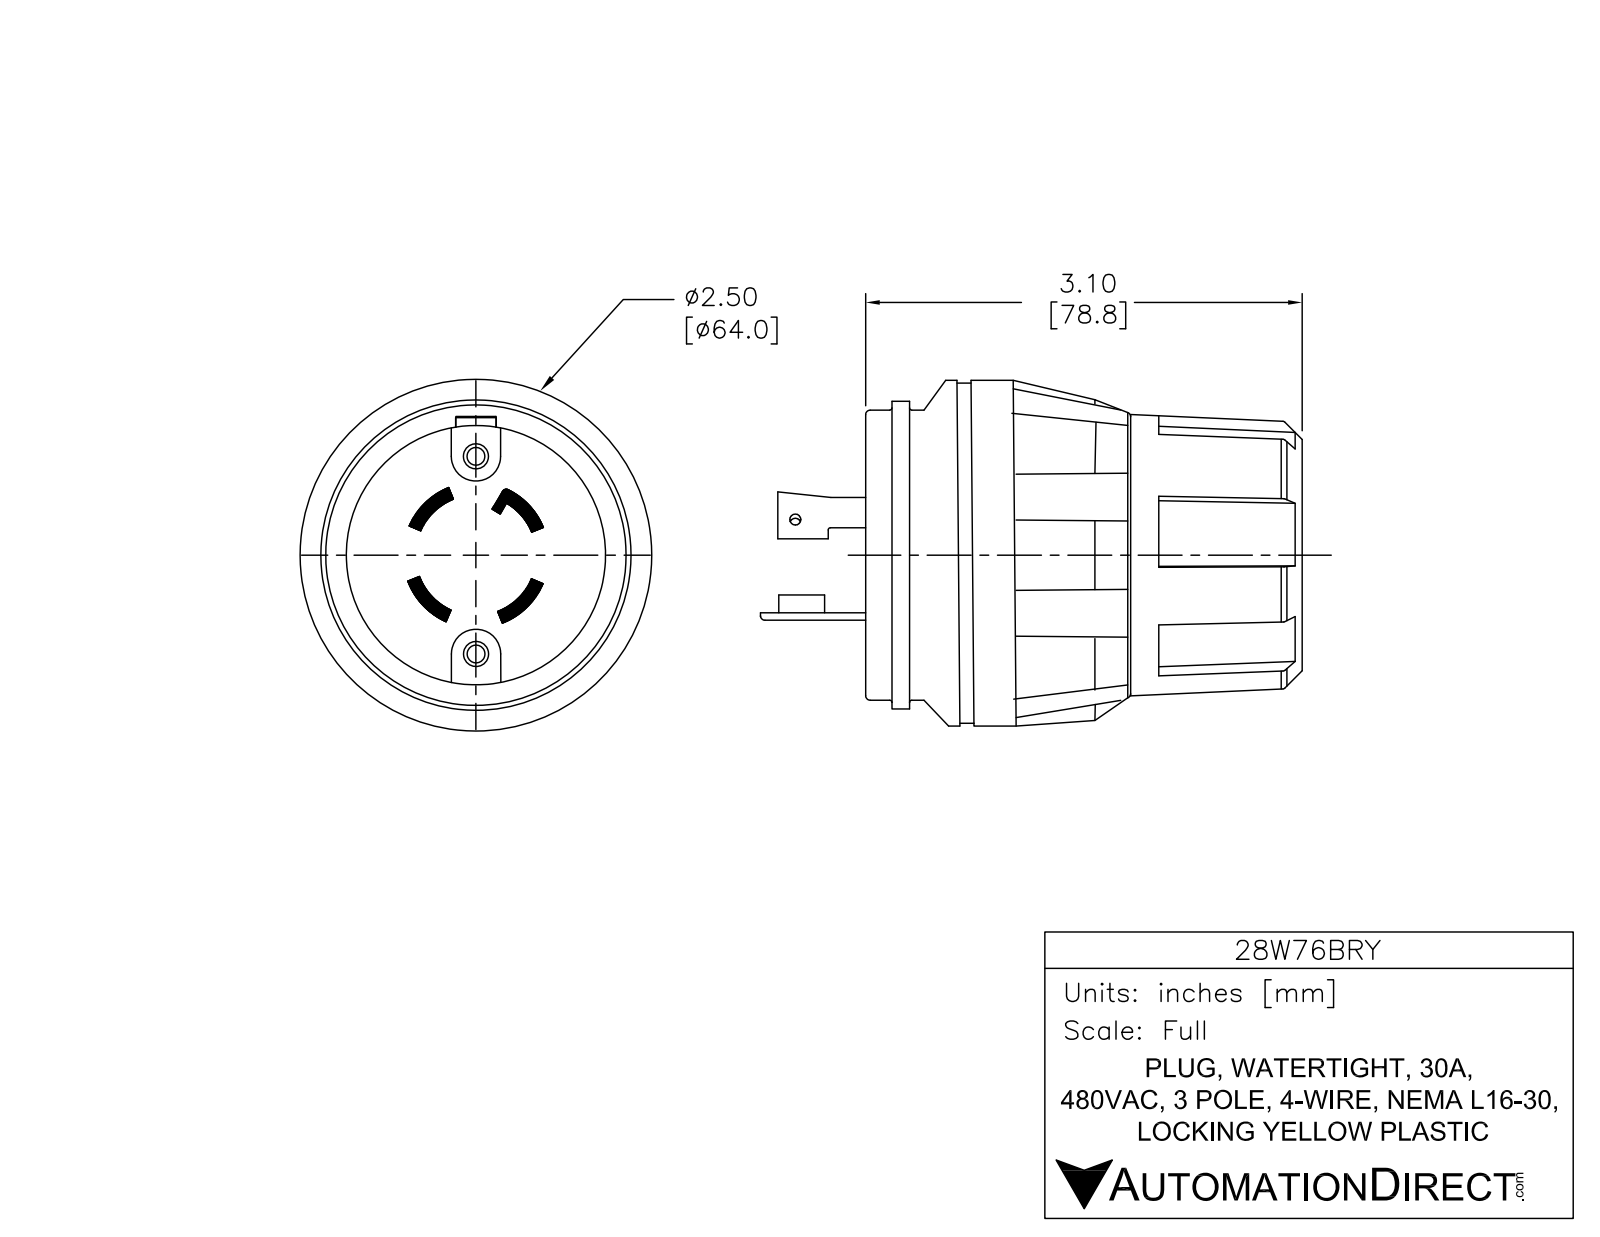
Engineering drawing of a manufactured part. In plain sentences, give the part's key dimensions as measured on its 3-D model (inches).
The part is named "28W76BRY". Its 3-D file was written by "SolidWorks 2013 (AUTOMOTIVE_DESIGN)". It is 1 solid with 210 faces: 81 planar, 56 cylindrical and 73 other. Overall it measures 4.147 by 2.5 by 2.5 inches. Its volume is 11.47 cubic inches and its surface area 42.37 square inches. Round holes: 2 of diameter 0.11, 1 of diameter 0.98, 1 of diameter 1.62, 1 of diameter 1.98. Round bosses or shafts: 2 of diameter 0.24, 1 of diameter 2.5, 1 of diameter 2.44, 1 of diameter 2.312, 1 of diameter 1.42. Partial cylindrical surfaces (rounded edges, fillets, slot ends): 11 of radius 0.03, 2 of radius 0.14, 1 of radius 0.06, 1 of radius 0.415, 1 of radius 0.475. The main face-to-face distances are 1.917, 2.037, 0.12, 3.247, 1.33, 1.21, 0.013, 1.93, 2.05, 3.26.
